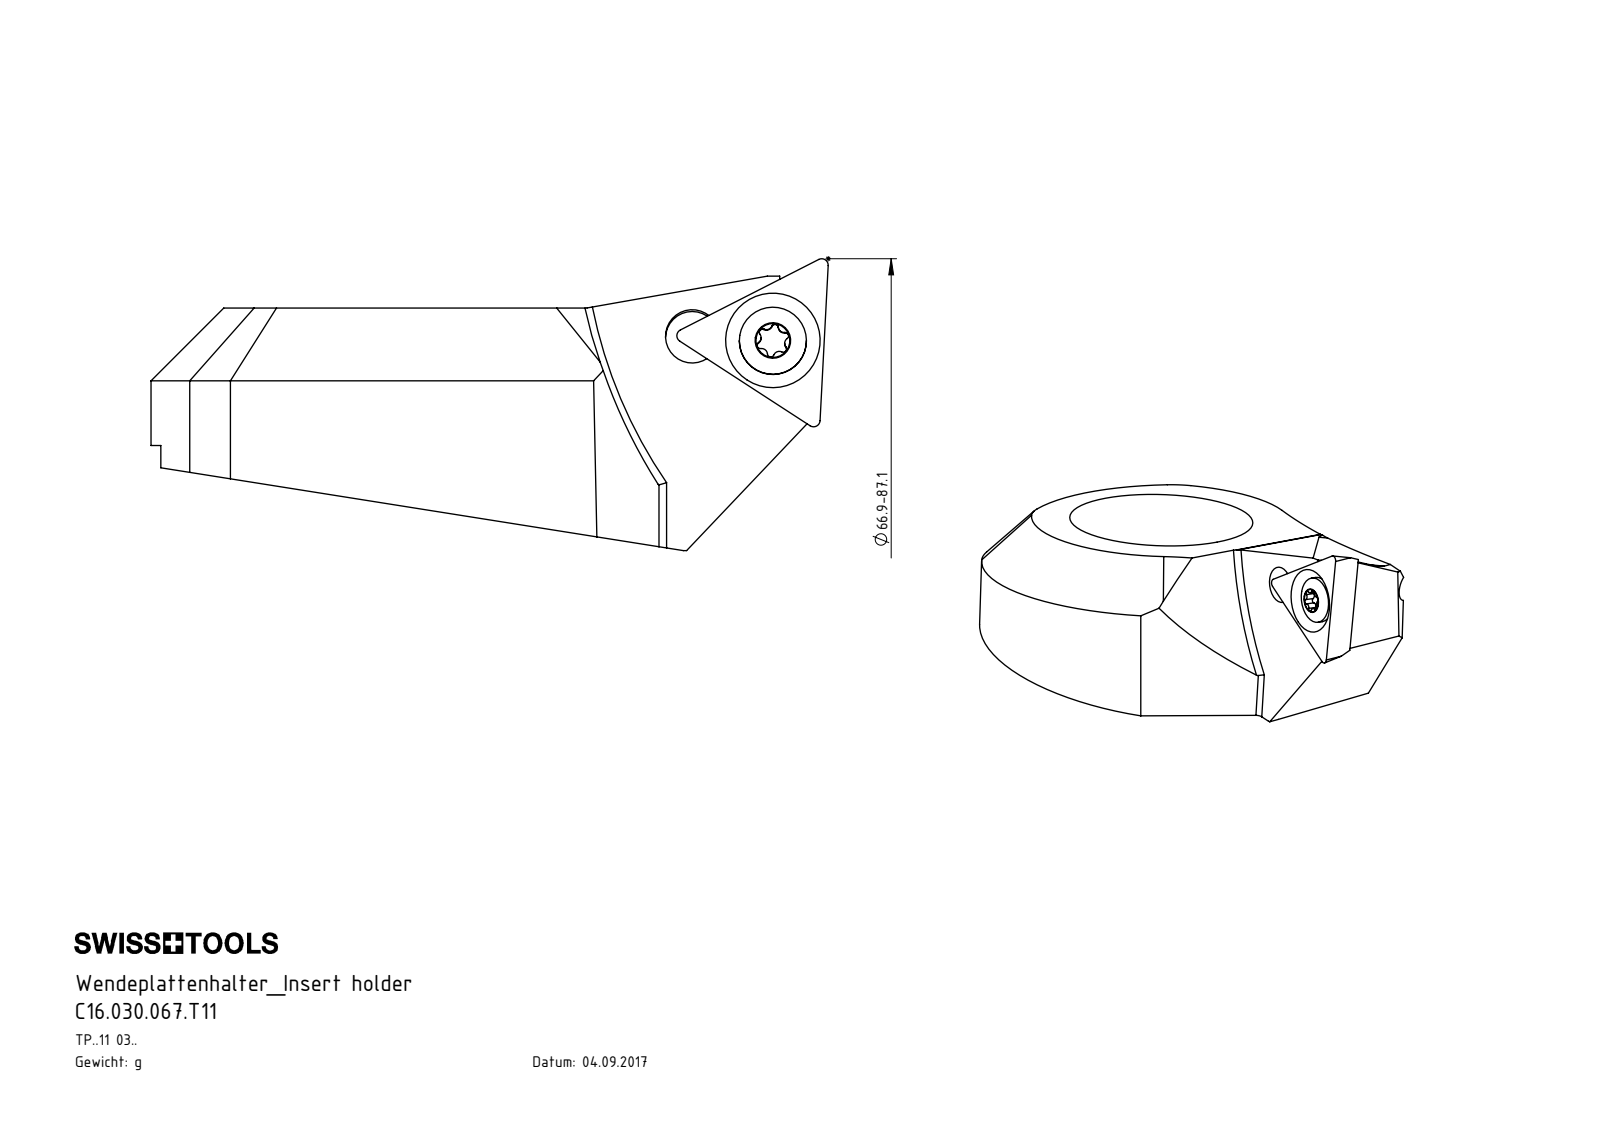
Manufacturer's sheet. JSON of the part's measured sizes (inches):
{"part_name": "WCA-ER2.001.007_A; F55-WTI.001.013_A_fertigbearbeitet; C16.030.067.T11; TPGH110304", "step_written_by": "SolidWorks 2017 (AUTOMOTIVE_DESIGN)", "units": "inches", "bodies": {"solids": 3, "faces": 107, "planar": 32, "cylindrical": 43, "other": 32}, "overall_size": [1.65, 1.303, 0.711], "volume_in3": 0.446, "surface_area_in2": 6.119, "round_holes": [[0.098, 1], [0.125, 1], [0.13, 1], [0.433, 1], [0.669, 1], [1.181, 1]], "round_bosses_or_shafts": [[0.163, 1], [0.118, 1]], "partial_cylinders_radius": [[0.008, 6], [0.014, 5], [0.02, 2], [0.394, 2], [0.014, 1], [0.118, 1], [0.197, 1], [0.652, 1]], "face_to_face_distances": [0.394, 0.236, 0.157, 0.335, 0.098, 0.059, 0.113, 0.125, 0.288, 0.276], "hole_center_spacings": [0.191, 0.197]}
